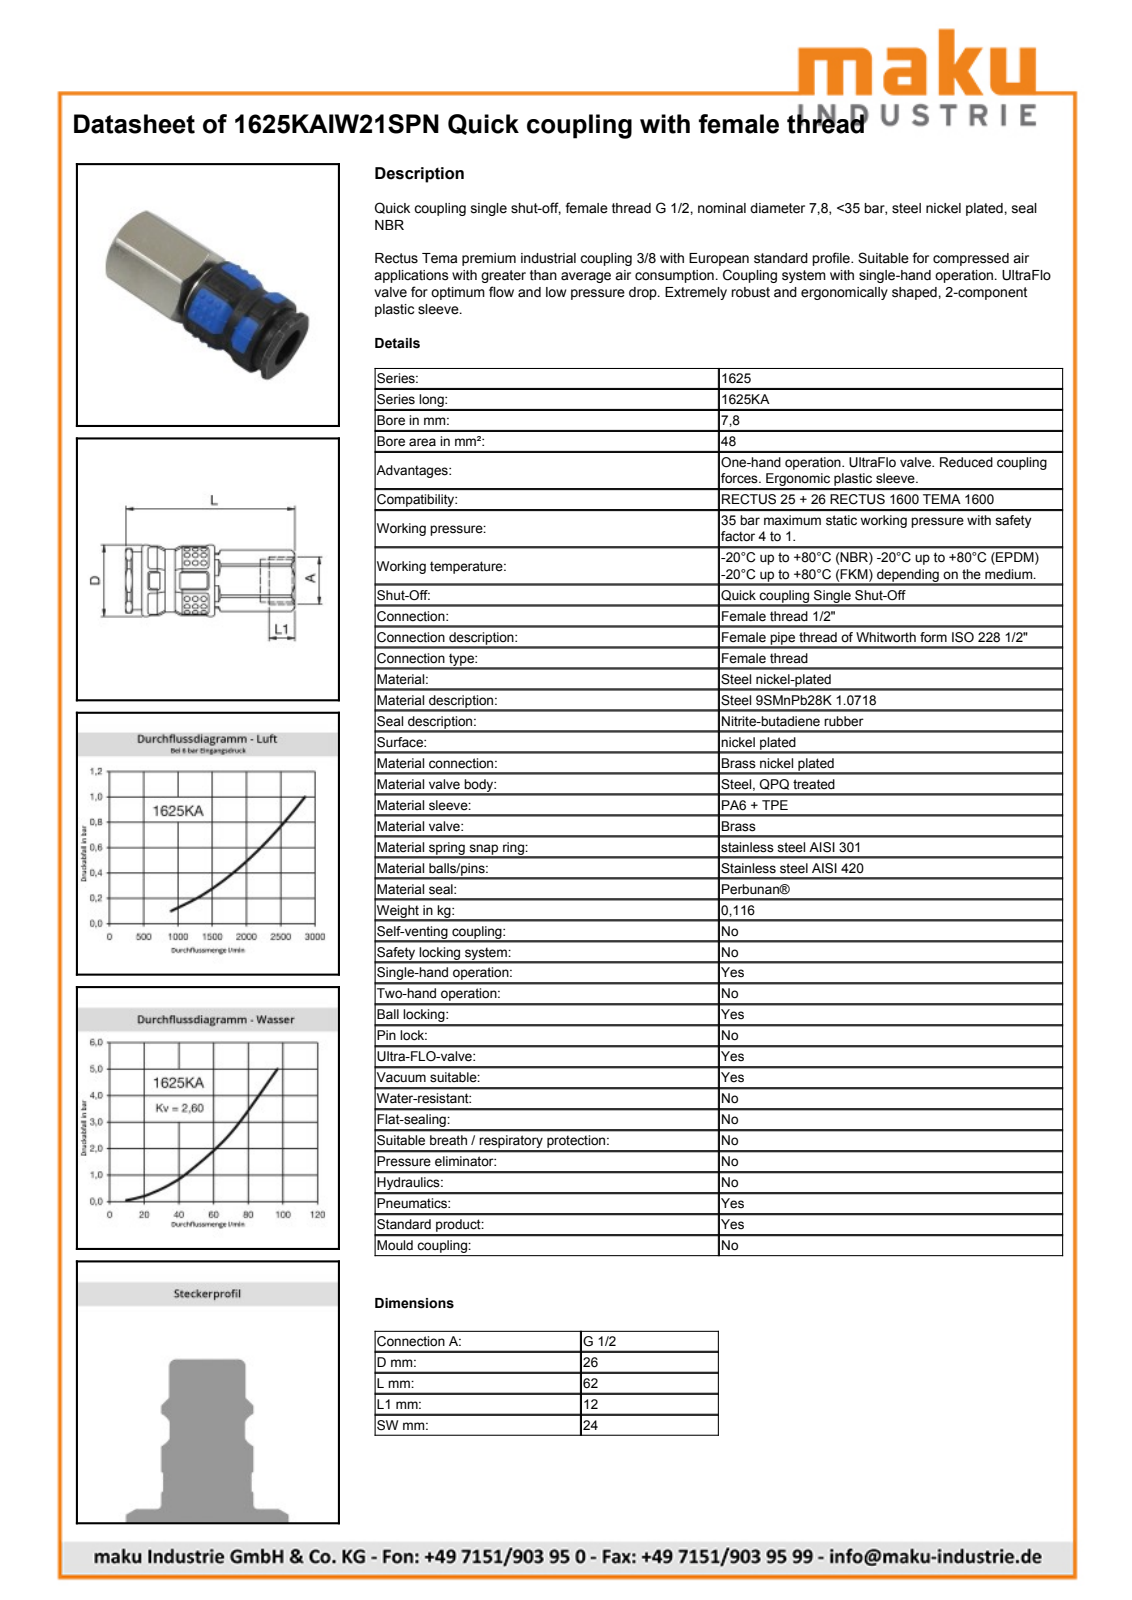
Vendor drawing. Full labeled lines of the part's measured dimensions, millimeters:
Part name (STEP PRODUCT): D105569
STEP written by: Autodesk Inventor 2011 (AUTOMOTIVE_DESIGN)
Units: millimetres
Bodies: 2 solids, 944 faces (351 planar, 148 cylindrical, 445 other)
Overall size (bounding box): 61.79 × 26.95 × 25.41
Volume: 23 020 mm³ · Surface area: 10 456 mm²
Round holes (diameter × count): ⌀1 ×4, ⌀17.2 ×1, ⌀17.9 ×1, ⌀18.63 ×1, ⌀19.6 ×1, ⌀20.7 ×1
Round bosses / shafts (diameter × count): ⌀25 ×1, ⌀22 ×1, ⌀20.3 ×1, ⌀19.3 ×1, ⌀17.6 ×1, ⌀17 ×1
Partial cylindrical surfaces — rounded edges, fillets, slot ends (radius × count): R0.4 ×8, R8.18 ×1, R11.2 ×1, R11.25 ×1, R11.5 ×1, R12 ×1, R12.3 ×1, R13.53 ×1
Main face-to-face distances: 24, 46.79, 61.79, 15, 30.93, 15.86, 30.86, 5.63, 25.3, 41.16
Hole centre spacings: 12.8
